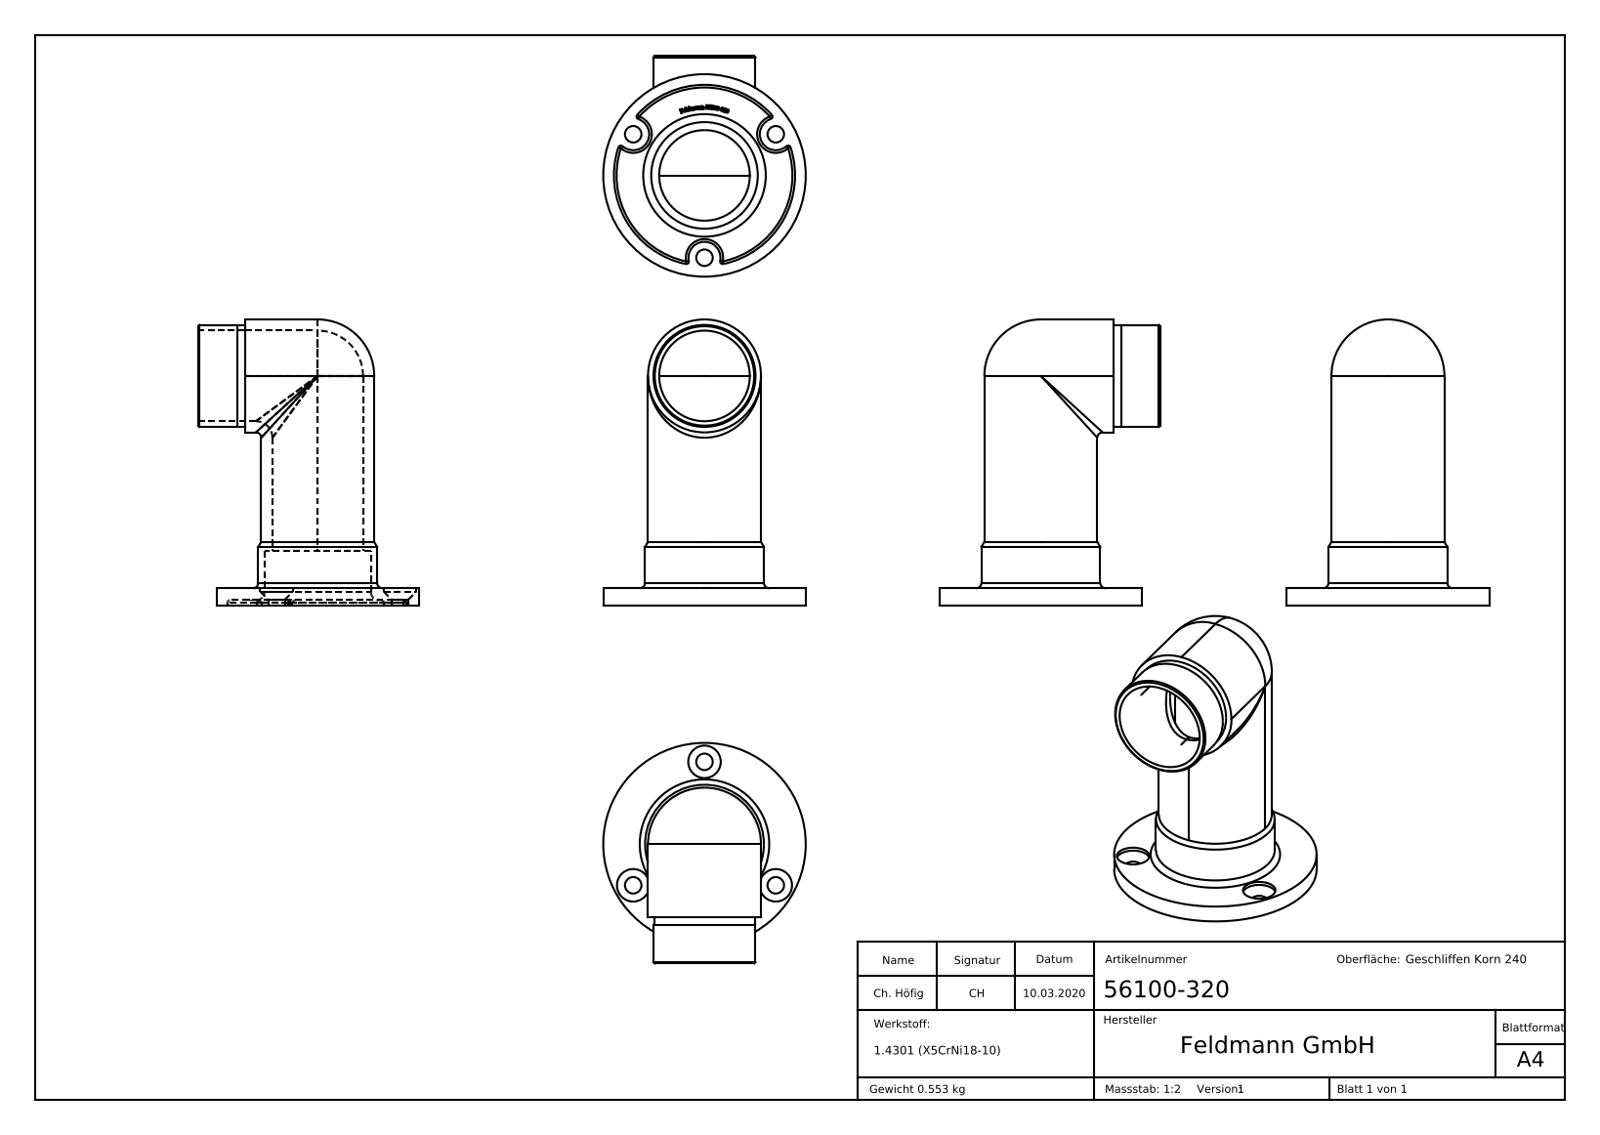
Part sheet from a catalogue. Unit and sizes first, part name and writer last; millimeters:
Units: millimetres
Overall size (bounding box): 107.4 × 82.8 × 76
Round holes (diameter × count): ⌀6.2 ×3, ⌀12.2 ×3, ⌀34 ×2, ⌀40 ×1, ⌀68 ×1
Round bosses / shafts (diameter × count): ⌀42.4 ×2, ⌀76 ×1, ⌀44.6 ×1, ⌀38.3 ×1, ⌀37.9 ×1
Partial cylindrical surfaces — rounded edges, fillets, slot ends (radius × count): R1 ×6, R6 ×3
Main face-to-face distances: 4.5, 2, 6.5, 20.5, 18.5, 14, 17.5, 3, 14.5, 2.1
Hole centre spacings: 30.9, 53.52
Volume: 70 006 mm³ · Surface area: 38 932 mm²
Bodies: 1 solid, 288 faces (113 planar, 36 cylindrical, 139 other)
Part name (STEP PRODUCT): 56100-320
STEP written by: SolidWorks 2015 (CONFIG_CONTROL_DESIGN)
